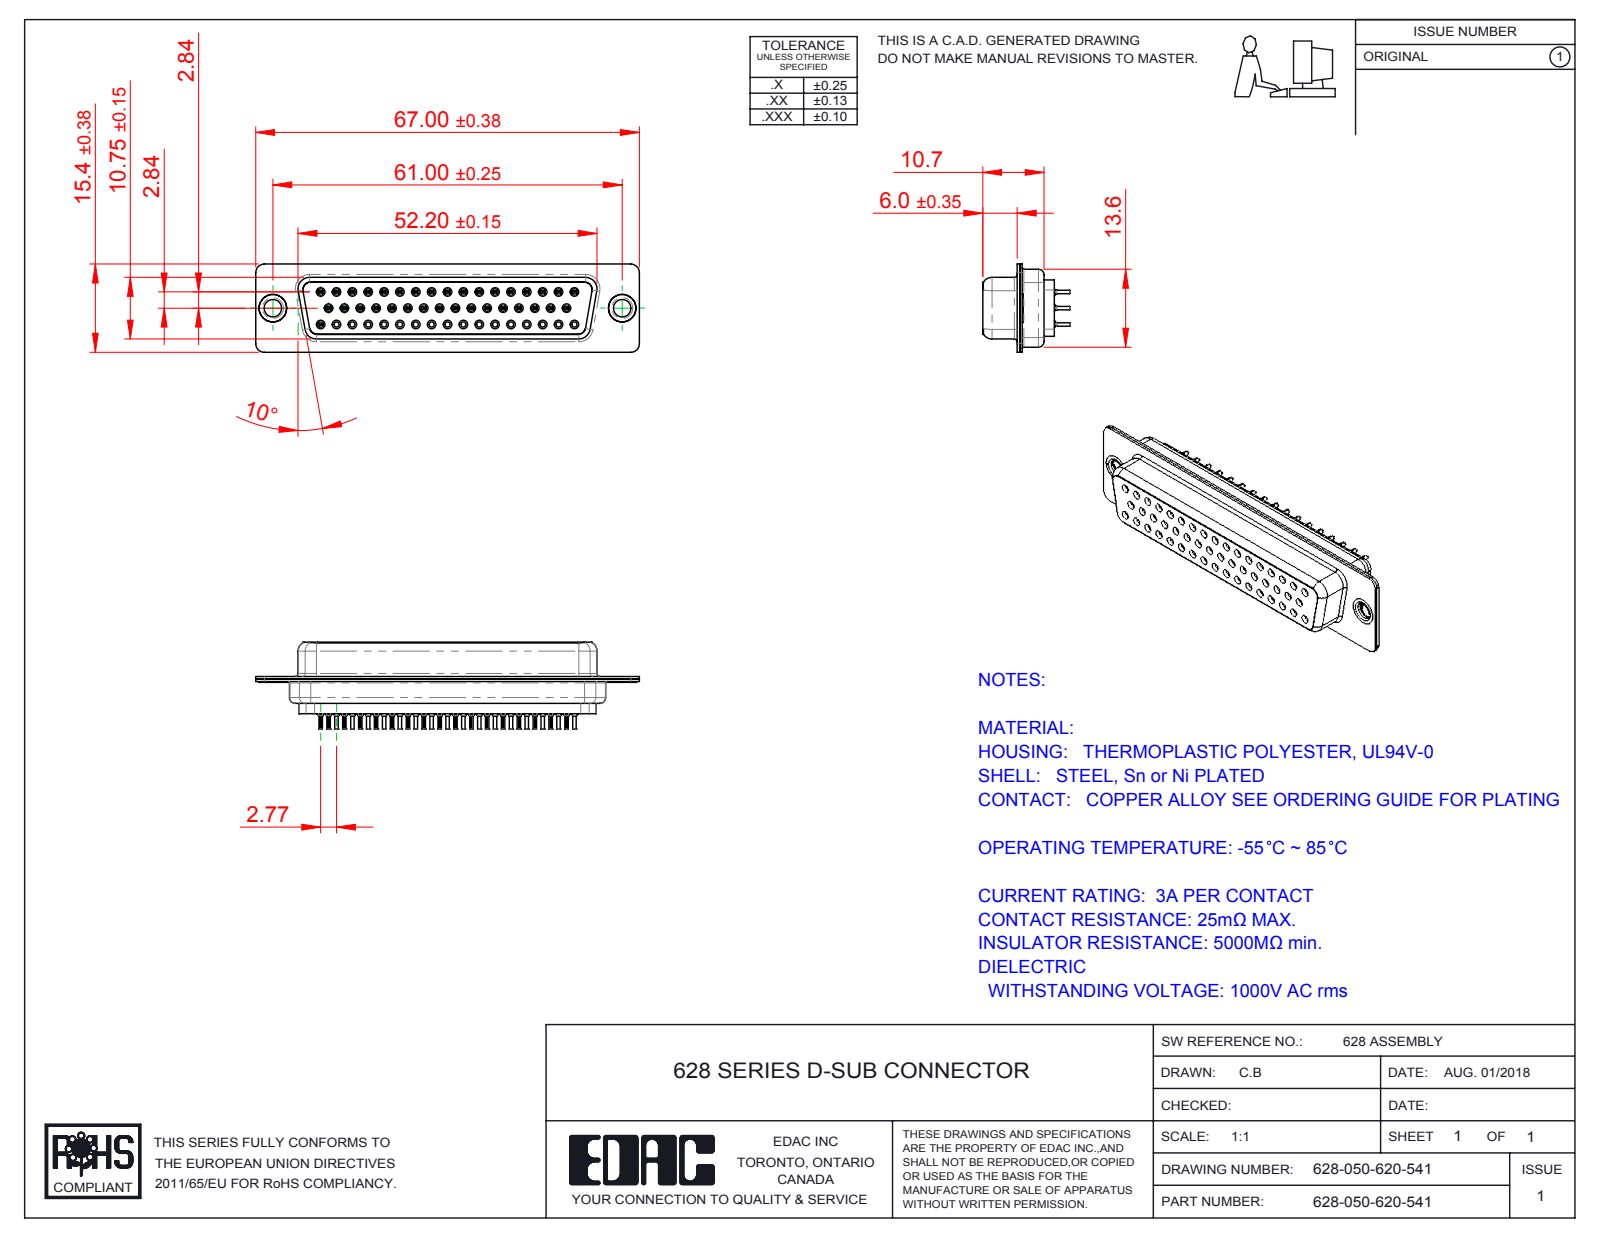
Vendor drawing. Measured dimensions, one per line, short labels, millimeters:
name: 628 Shell Rear_50 Contacts; 628 Contact Row 2_20L; 628 Contact Row 3_20L; 628-050-620-541 (+4 more)
written by: SolidWorks 2016 (CONFIG_CONTROL_DESIGN)
unit: mm
bodies: 39 solids, 4779 faces (1169 planar, 1371 cylindrical, 2239 other)
size: 67 × 15.4 × 15.2
volume: 6 502 mm³; area: 13 441 mm²
holes: 50× ⌀0.9, 50× ⌀1.6, 34× ⌀0.2, 34× ⌀0.8, 34× ⌀1.1, 17× ⌀1.7, 16× ⌀1.5, 16× ⌀2, 2× ⌀3.05, 2× ⌀4, 2× ⌀4.8
bosses: 34× ⌀2, 34× ⌀1.5, 34× ⌀1.2, 34× ⌀0.6, 2× ⌀5, 2× ⌀4.9, 2× ⌀3.55
rounds: 68× R0.1, 33× R0.28, 16× R1.5, 12× R2, 8× R1.35, 4× R0.25, 4× R0.5, 4× R0.6
face distances: 0.45, 0.4, 10.3, 6.05, 0.9, 6.5, 6.45, 6, 12.5, 11.33
hole spacings: 3.16, 2.77, 5.54, 8.31, 11.08, 13.85, 16.62, 19.39
